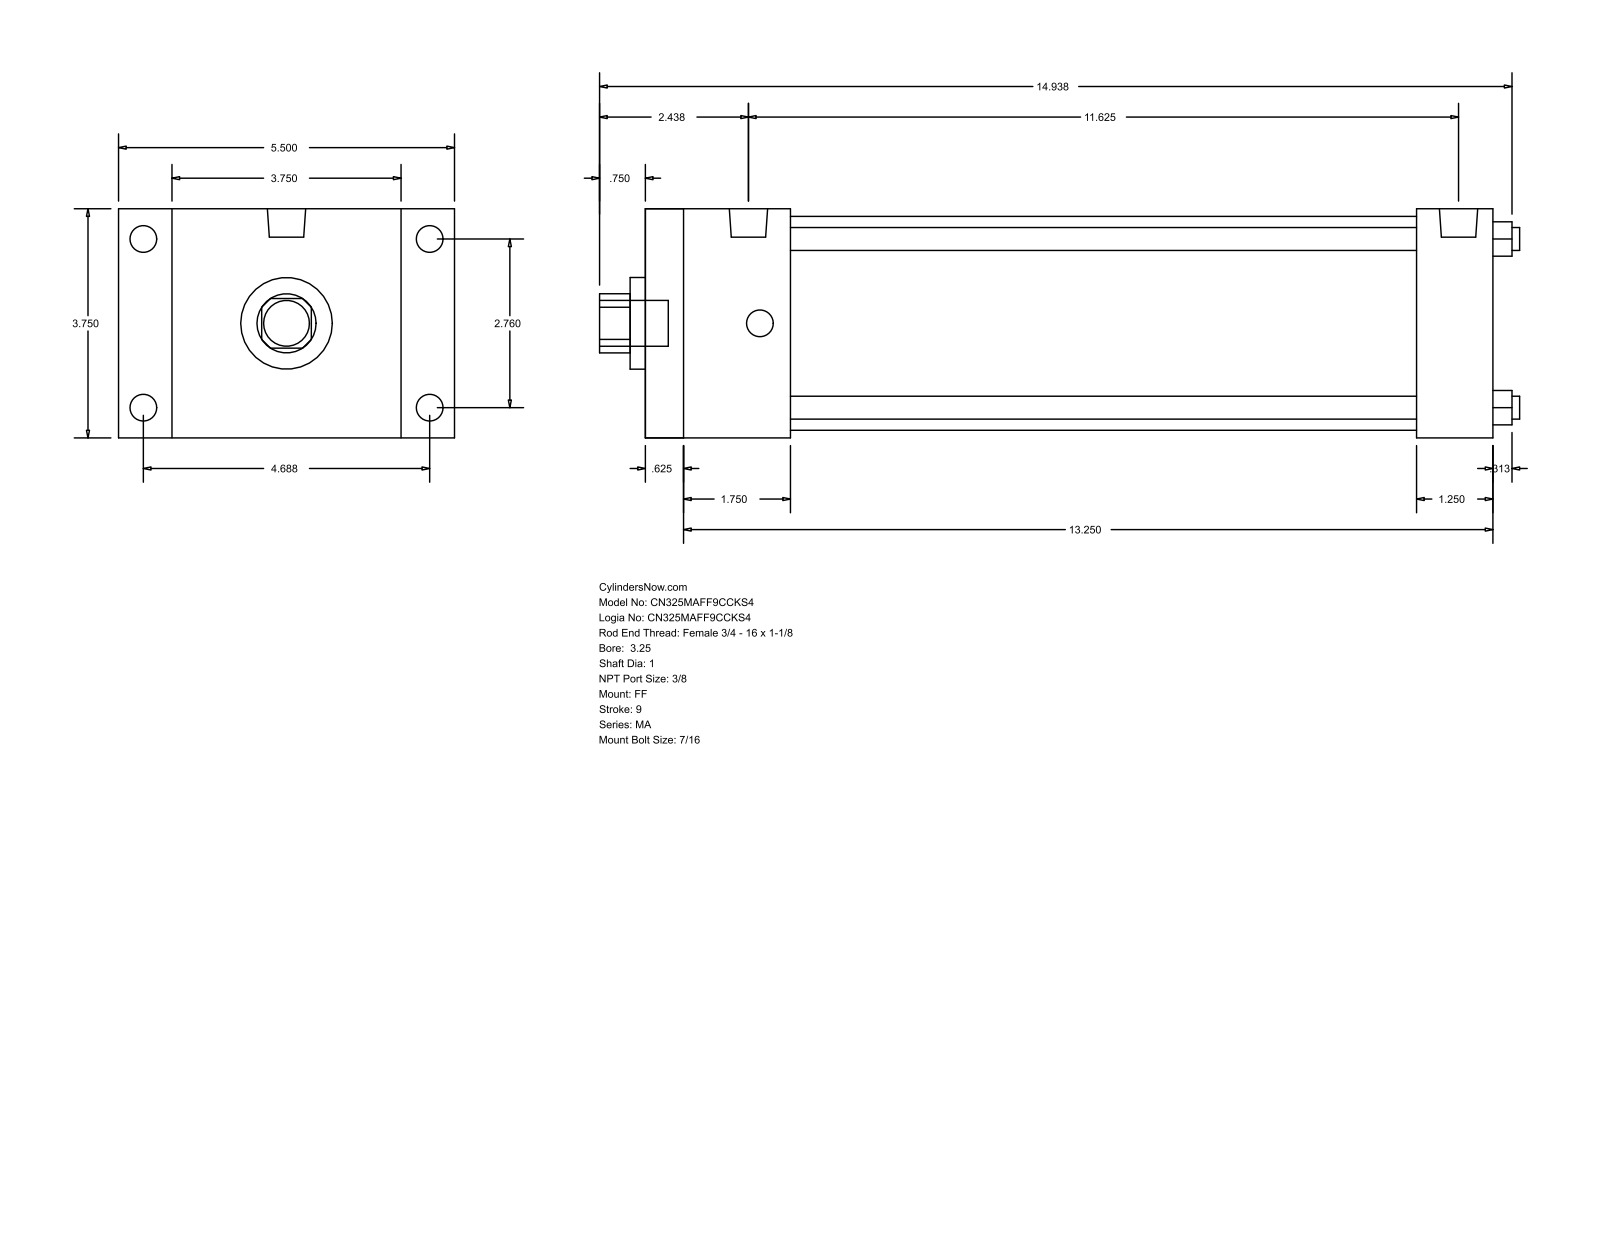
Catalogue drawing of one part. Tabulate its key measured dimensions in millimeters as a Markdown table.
| quantity | value |
| --- | --- |
| part name | MA_FF__0325_1 |
| STEP written by | GSSL Pune (CONFIG_CONTROL_DESIGN) |
| units | millimeters |
| bodies | 0 solids, 92 faces (64 planar, 28 cylindrical, 0 other) |
| overall size | 382.59 × 139.7 × 95.25 |
| round holes (diameter × count) | 9.53 × 4, 25.4 × 1, 38.1 × 1, 88.9 × 1 |
| round bosses / shafts (diameter × count) | 11.11 × 8, 15.93 × 2, 19.05 × 1 |
| partial cylindrical surfaces (radius × count) | 12.29 × 1 |
| main face-to-face distances | 95.24, 352.43, 15.87, 336.56, 22.23, 117.47, 60.33, 320.68, 44.46, 304.81 |
| hole center spacings | 49.57, 70.1, 99.14 |
